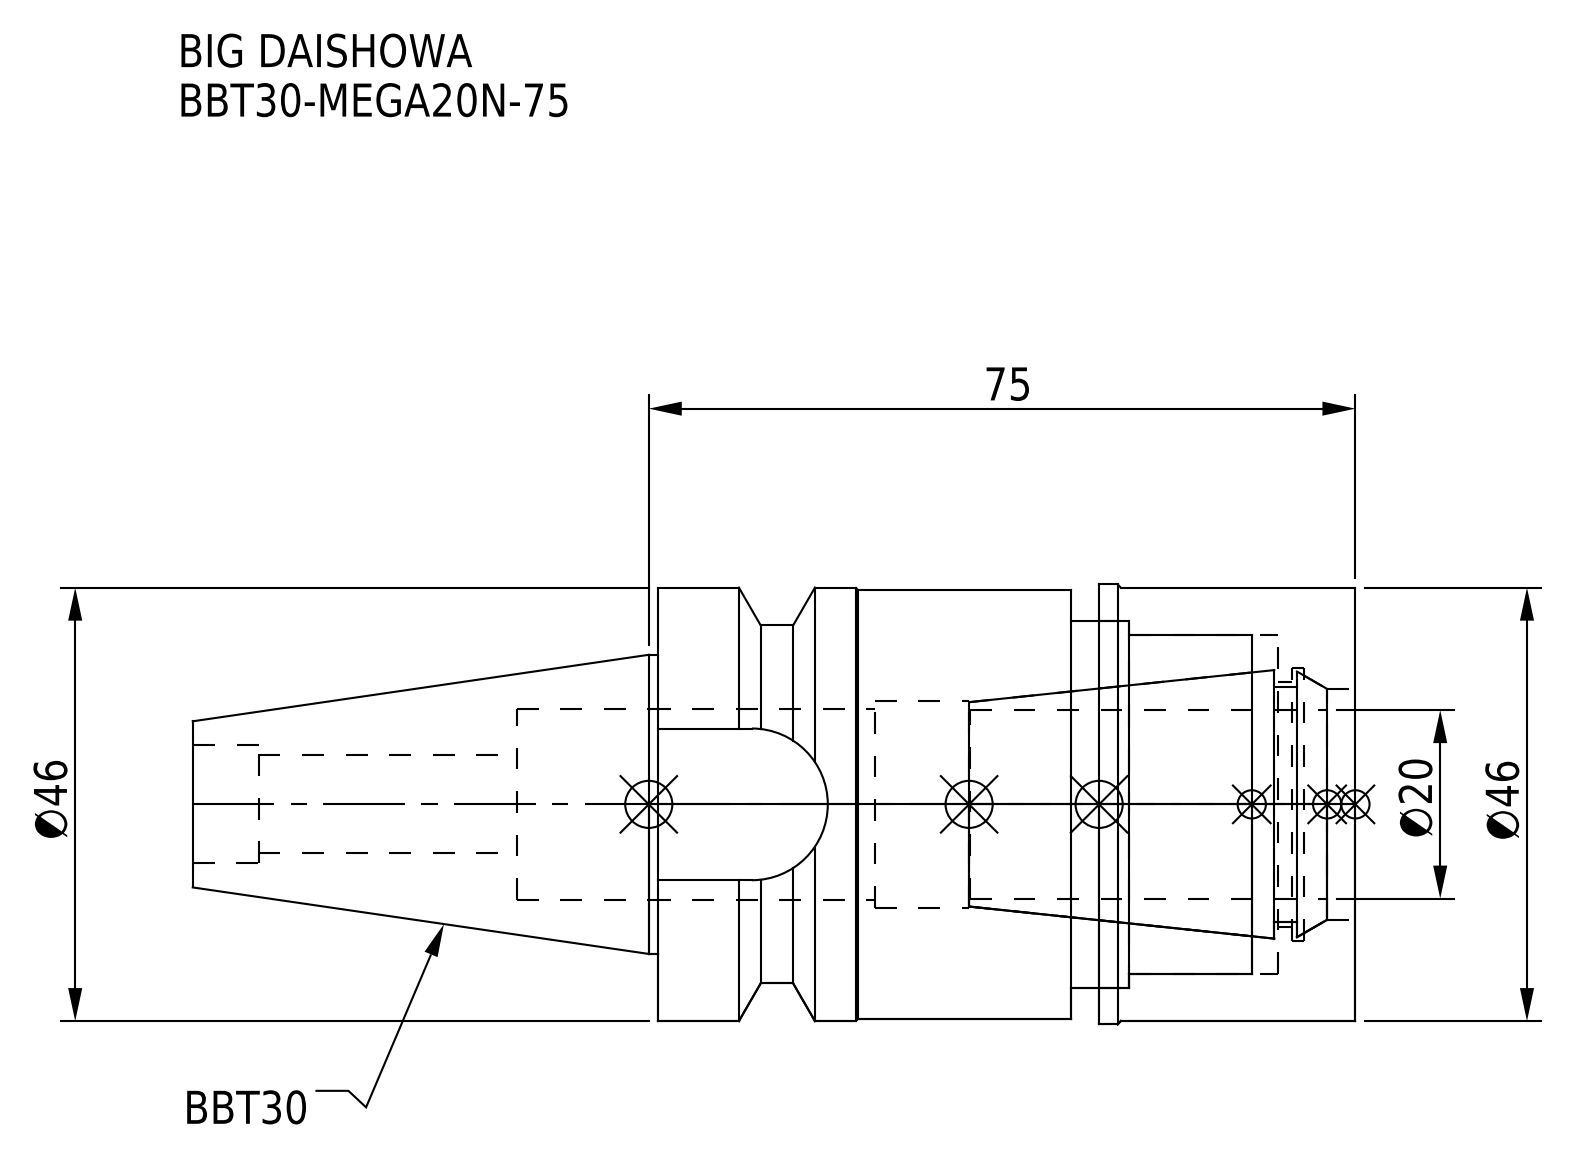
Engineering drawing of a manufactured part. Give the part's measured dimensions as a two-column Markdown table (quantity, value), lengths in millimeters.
| quantity | value |
| --- | --- |
| part name | DXF_TEMP_ASSY_ASM_4_ASM.stp; MGN20_1.stp; BBT30-MEGA20N-75-200.stp; BBT30-MEGA20N-75 (+3 more) |
| STEP written by | SolidWorks 2019 (CONFIG_CONTROL_DESIGN) |
| units | millimeters |
| bodies | 2 solids, 76 faces (22 planar, 40 cylindrical, 14 other) |
| overall size | 123.4 × 46.7 × 46.7 |
| volume | 98 713 mm³ |
| surface area | 31 353 mm² |
| round holes (diameter × count) | 10.4 × 1, 12.5 × 1, 20.3 × 1, 22 × 1, 24.5 × 1, 26 × 1, 29 × 1, 36 × 1, 39 × 1 |
| round bosses / shafts (diameter × count) | 46.7 × 1, 46 × 1, 45.5 × 1, 31.75 × 1 |
| partial cylindrical surfaces (radius × count) | 8.05 × 1, 19 × 1 |
| main face-to-face distances | 74, 27.2, 46.8, 8.2, 19, 65.8, 30.2, 22, 3, 43.8 |
